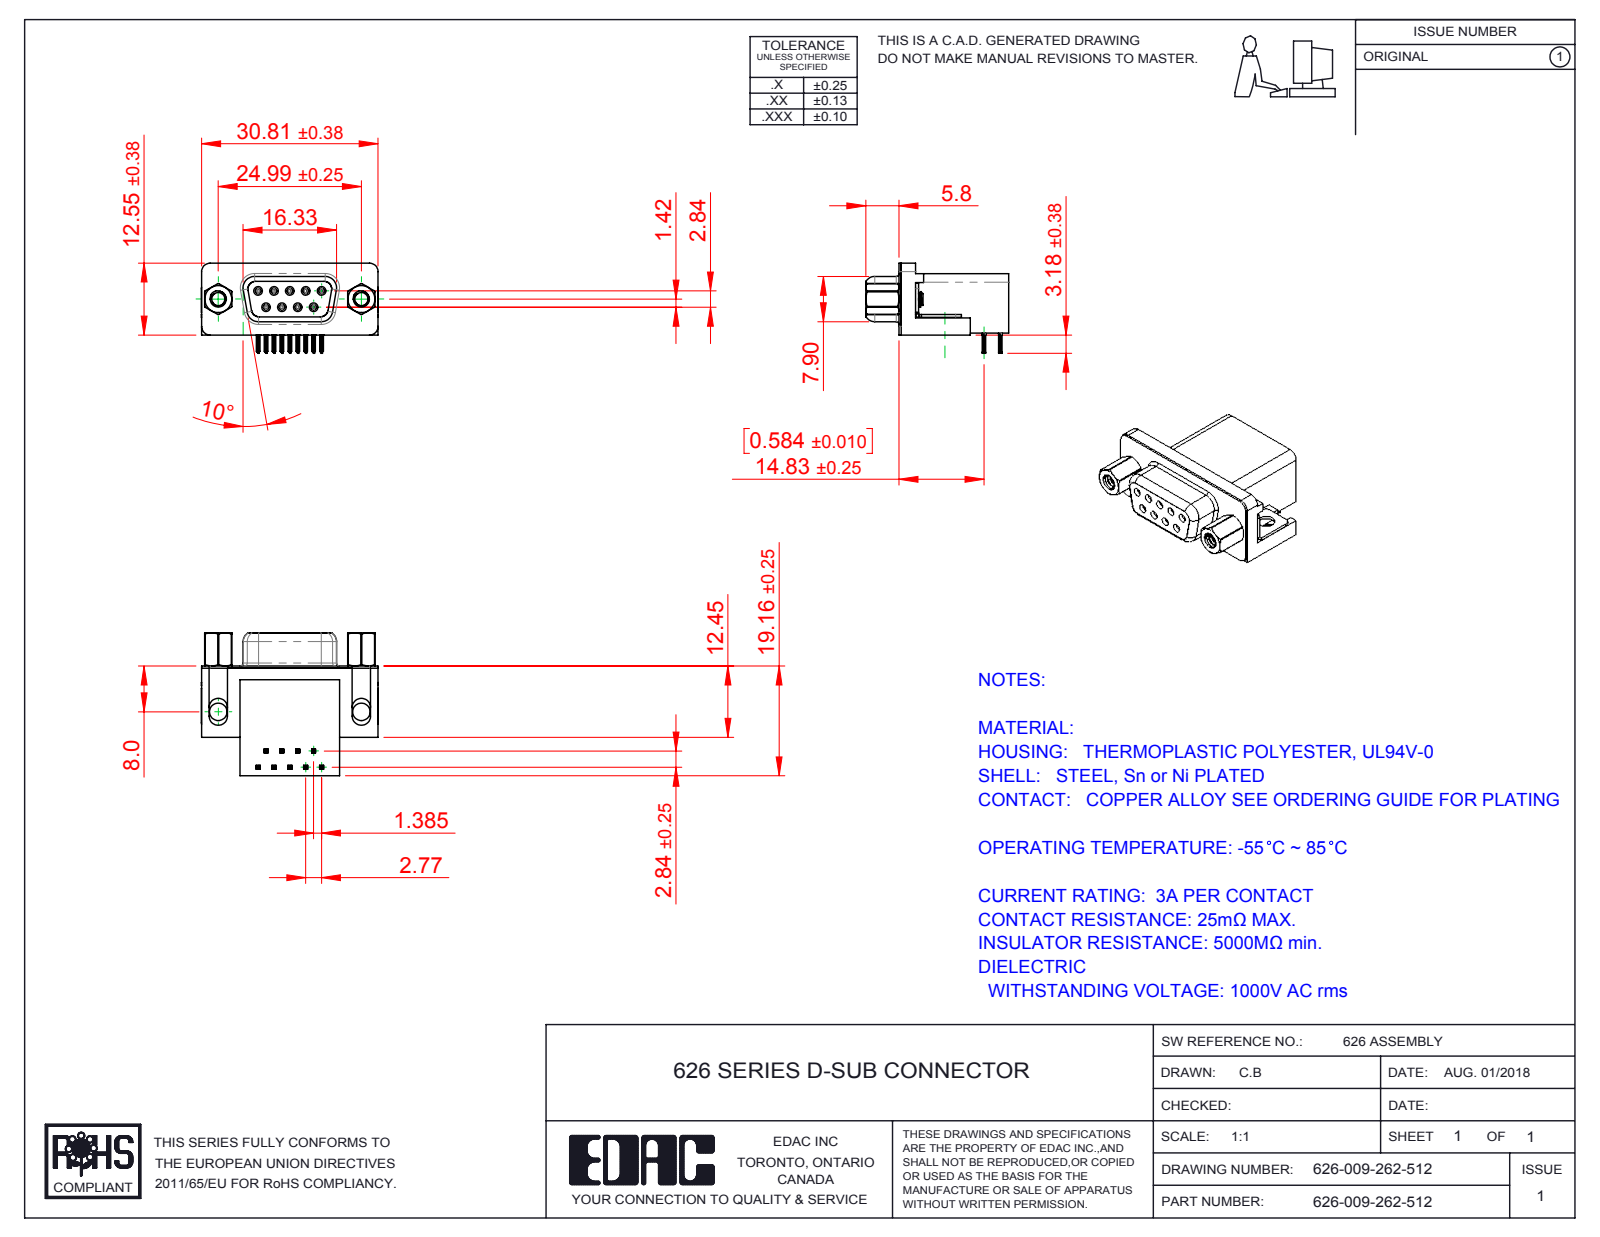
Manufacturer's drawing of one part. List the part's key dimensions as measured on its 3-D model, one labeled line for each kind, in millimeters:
Part name (STEP PRODUCT): 626 Contact Bottom; 626-009-262-512; 626 Shell_9 Socket; 626 4-40 Hex Standoff 5 (+3 more)
STEP written by: SolidWorks 2016 (CONFIG_CONTROL_DESIGN)
Units: millimetres
Bodies: 15 solids, 1610 faces (690 planar, 450 cylindrical, 470 other)
Overall size (bounding box): 30.89 × 24.96 × 15.73
Volume: 5 097 mm³ · Surface area: 5 940 mm²
Round holes (diameter × count): ⌀0.8 ×9, ⌀0.9 ×9, ⌀2.29 ×2, ⌀3.05 ×2, ⌀4 ×2, ⌀4.8 ×2, ⌀5 ×2
Round bosses / shafts (diameter × count): ⌀1.2 ×9, ⌀4.9 ×2, ⌀2.79 ×2
Partial cylindrical surfaces — rounded edges, fillets, slot ends (radius × count): R0.1 ×72, R0.15 ×36, R0.35 ×18, R1 ×18, R0.34 ×9, R1.35 ×8, R1.6 ×8, R1.5 ×7
Main face-to-face distances: 0.4, 10.34, 0.35, 18.76, 19.16, 16.26, 2.9, 2.5, 6.2, 5.8
Hole centre spacings: 3.16, 2.77, 5.54, 5.03, 5.04, 8.31, 7.48, 7.49
